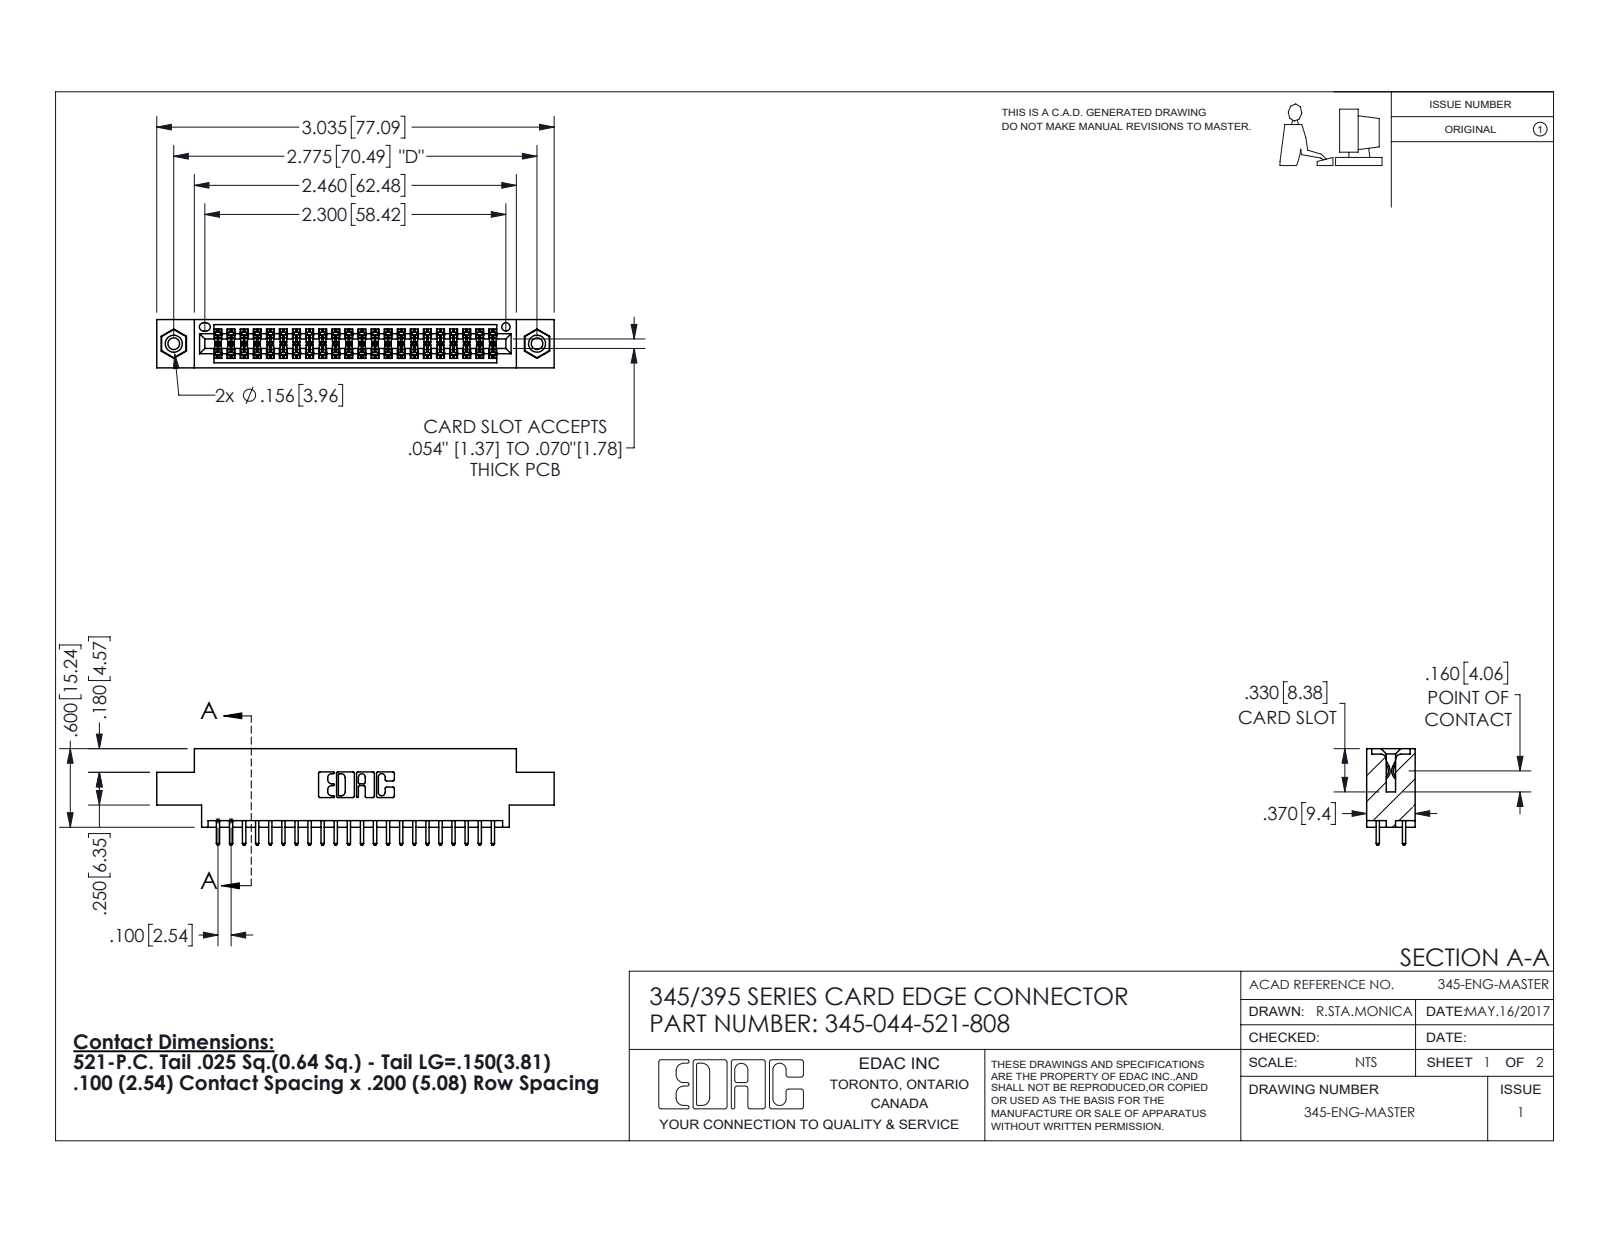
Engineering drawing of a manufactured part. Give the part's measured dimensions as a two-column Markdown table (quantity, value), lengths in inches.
| quantity | value |
| --- | --- |
| part name | 345-044-521-808; 345-250-001_345-250-003-102; 345 Part_0.170 Offset - 0.156 Dia-TI; 345-292-001_345-293-121 |
| STEP written by | SolidWorks 2016 (CONFIG_CONTROL_DESIGN) |
| units | inches |
| bodies | 47 solids, 2390 faces (1568 planar, 806 cylindrical, 16 other) |
| overall size | 3.035 × 0.737 × 0.37 |
| volume | 0.437 in³ |
| surface area | 15.88 in² |
| round holes (diameter × count) | 0.089 × 2, 0.125 × 2, 0.156 × 2, 0.064 × 1 |
| round bosses / shafts (diameter × count) | 0.155 × 2 |
| partial cylindrical surfaces (radius × count) | 0.006 × 66, 0.01 × 44, 0.01 × 22, 0.007 × 6, 0.031 × 6, 0.026 × 3, 0.014 × 2, 0.019 × 2 |
| main face-to-face distances | 0.072, 0.298, 0.37, 0.2, 0.098, 0.272, 0.025, 0.225, 0.175, 0.149 |
| hole center spacings | 0.27, 2.541, 2.775 |
